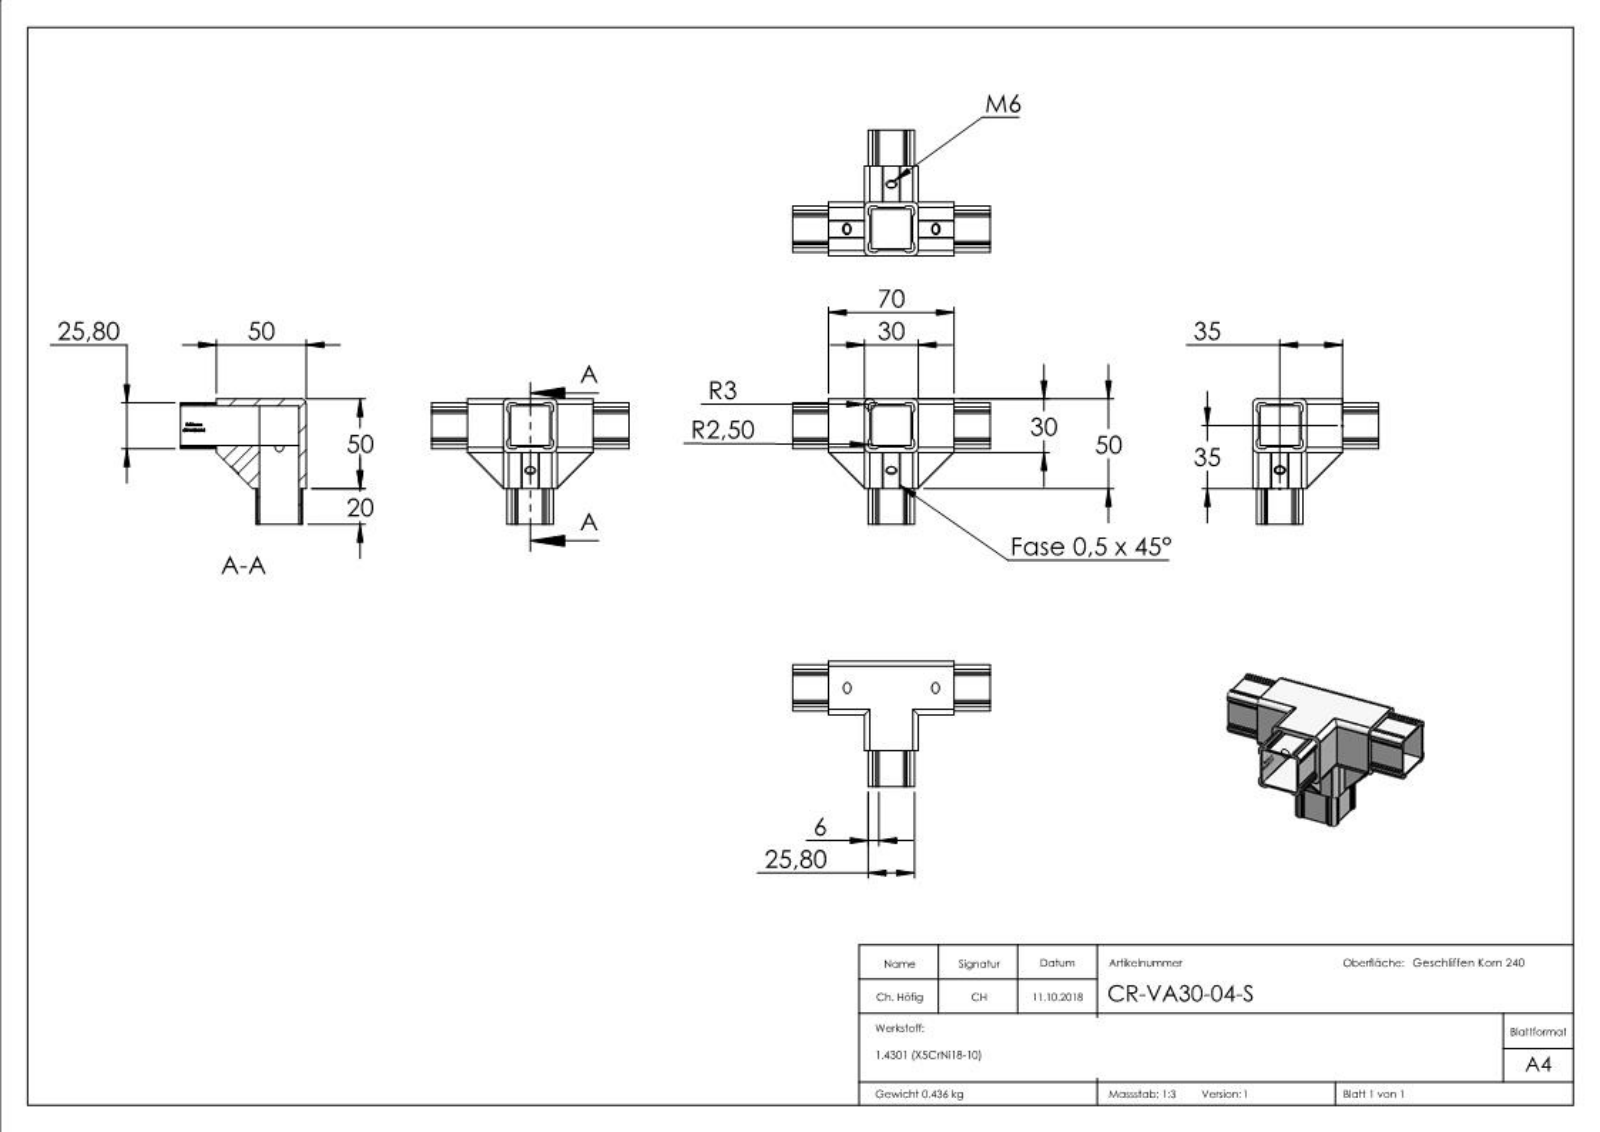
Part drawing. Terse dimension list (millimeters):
name: CR-VA30-04-S
written by: SolidWorks 2015 (CONFIG_CONTROL_DESIGN)
unit: mm
bodies: 1 solid, 461 faces (245 planar, 101 cylindrical, 115 other)
size: 110 × 70 × 70
volume: 55 197 mm³; area: 38 723 mm²
holes: 3× ⌀5
rounds: 48× R1, 12× R2.5, 12× R3
face distances: 4, 26, 22, 0.9, 3.1, 26.9, 22.9, 30, 20, 23.8
